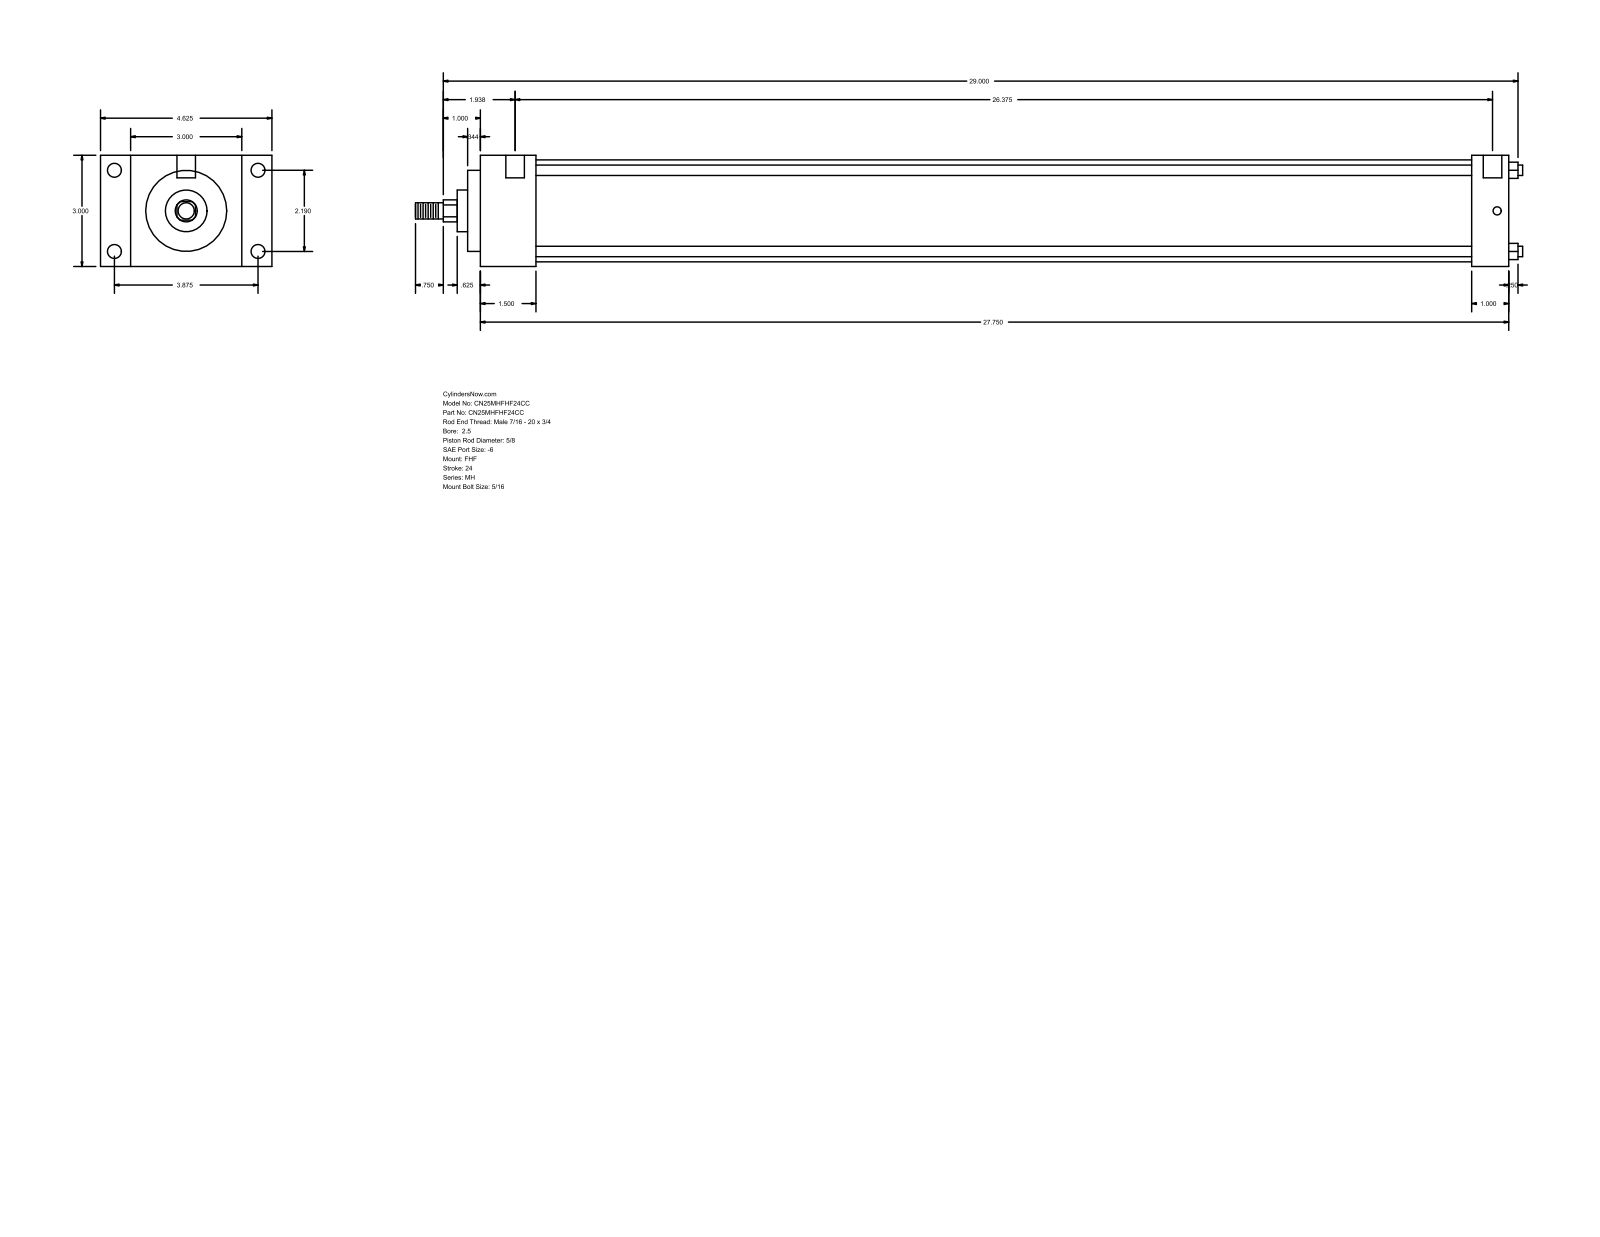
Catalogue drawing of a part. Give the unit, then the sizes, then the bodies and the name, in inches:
Units: inches
Overall size (bounding box): 29.875 × 4.625 × 3
Round holes (diameter × count): ⌀0.219 ×4, ⌀0.375 ×4, ⌀0.5 ×2
Round bosses / shafts (diameter × count): ⌀0.281 ×4, ⌀2.75 ×1, ⌀2.187 ×1, ⌀1.125 ×1, ⌀0.625 ×1, ⌀0.437 ×1
Partial cylindrical surfaces — rounded edges, fillets, slot ends (radius × count): R0.297 ×1
Main face-to-face distances: 3, 27.75, 1.5, 26.25, 0.813, 3.813, 4.625, 1, 26.75, 25.25
Hole centre spacings: 2.19, 3.875, 4.451, 26.687, 0.125, 0.187, 26.375, 26.5
Bodies: 0 solids, 90 faces (61 planar, 29 cylindrical, 0 other)
Part name (STEP PRODUCT): MH_FHF__0250_0.625
STEP written by: GSSL Pune (CONFIG_CONTROL_DESIGN)
